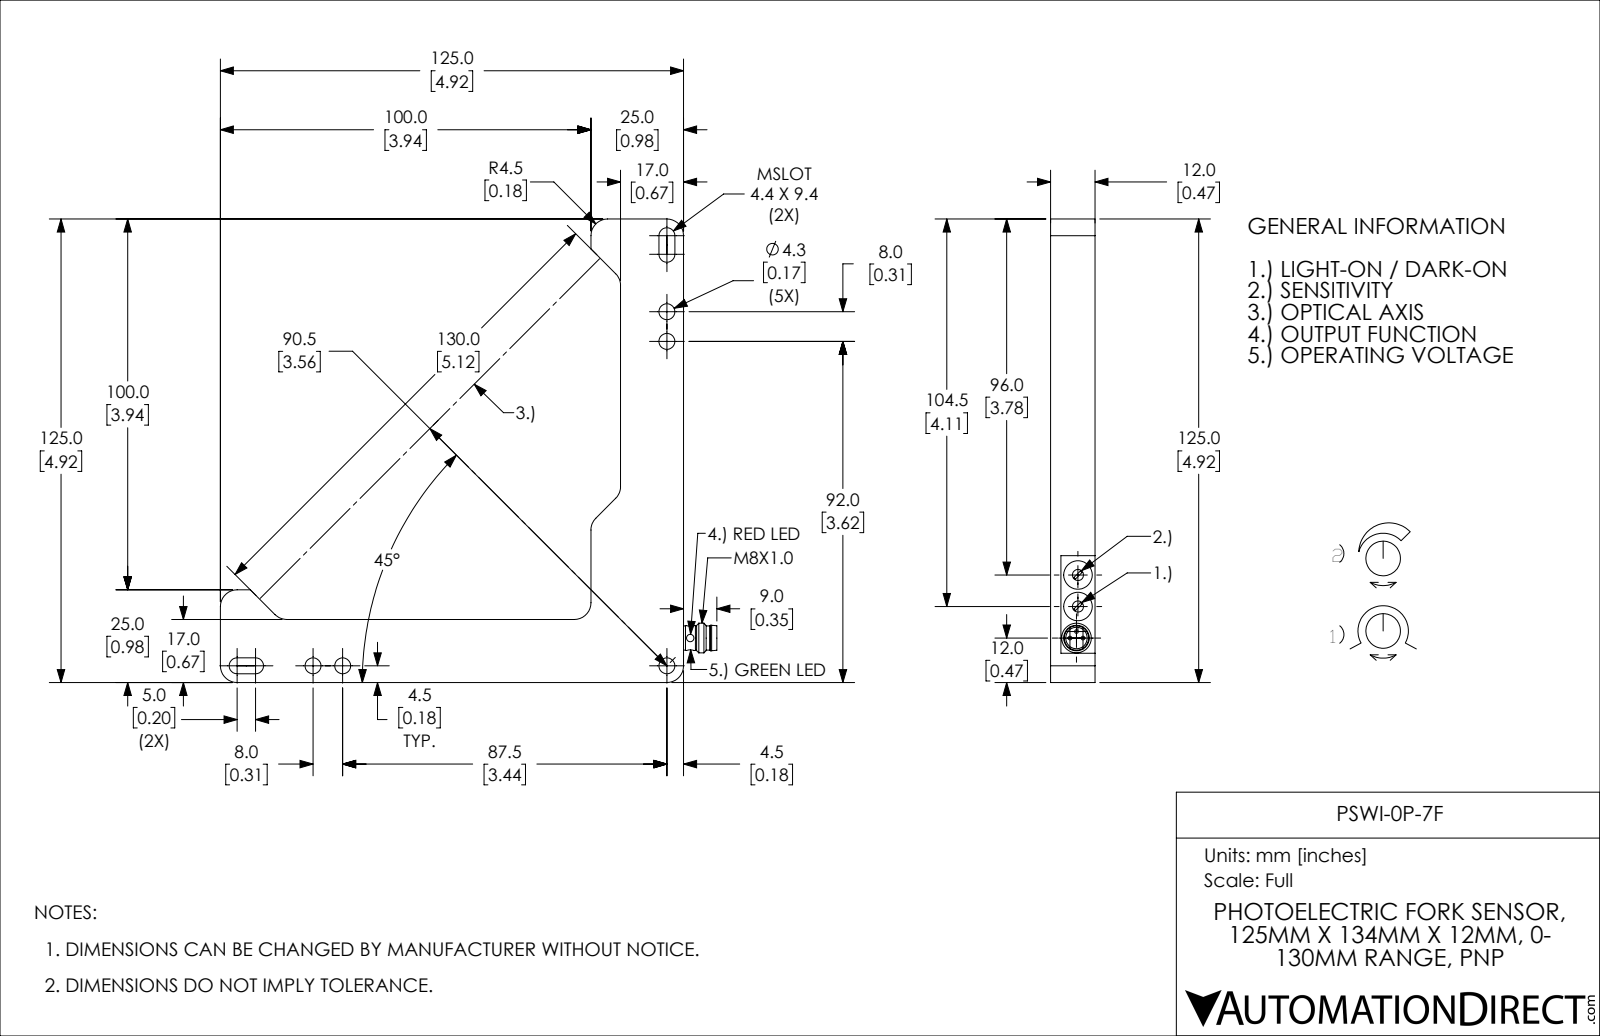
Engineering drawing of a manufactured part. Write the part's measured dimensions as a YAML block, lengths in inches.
part_name: "PSWI-0P-7F"
step_written_by: "SolidWorks 2017 (AUTOMOTIVE_DESIGN)"
units: inches
bodies: {solids: 1, faces: 90, planar: 42, cylindrical: 41, other: 7}
overall_size: [5.276, 4.921, 0.472]
volume: 3.111
surface_area: 25.24
round_holes:
  - {diameter: 0.169, count: 5}
  - {diameter: 0.079, count: 2}
  - {diameter: 0.118, count: 2}
  - {diameter: 0.303, count: 2}
  - {diameter: 0.228, count: 1}
round_bosses_or_shafts:
  - {diameter: 0.039, count: 3}
  - {diameter: 0.315, count: 1}
  - {diameter: 0.272, count: 1}
  - {diameter: 0.264, count: 1}
  - {diameter: 0.257, count: 1}
partial_cylinders:
  - {radius: 0.177, count: 10}
  - {radius: 0.085, count: 4}
  - {radius: 0.049, count: 2}
face_to_face_distances: [0.472, 0.669, 4.921, 4.252, 0.984, 0.315, 3.937, 0.262, 0.407, 4.659]
hole_center_spacings: [0.315, 3.445, 3.76, 5.099, 0.335, 0.335, 0.385, 0.669]
